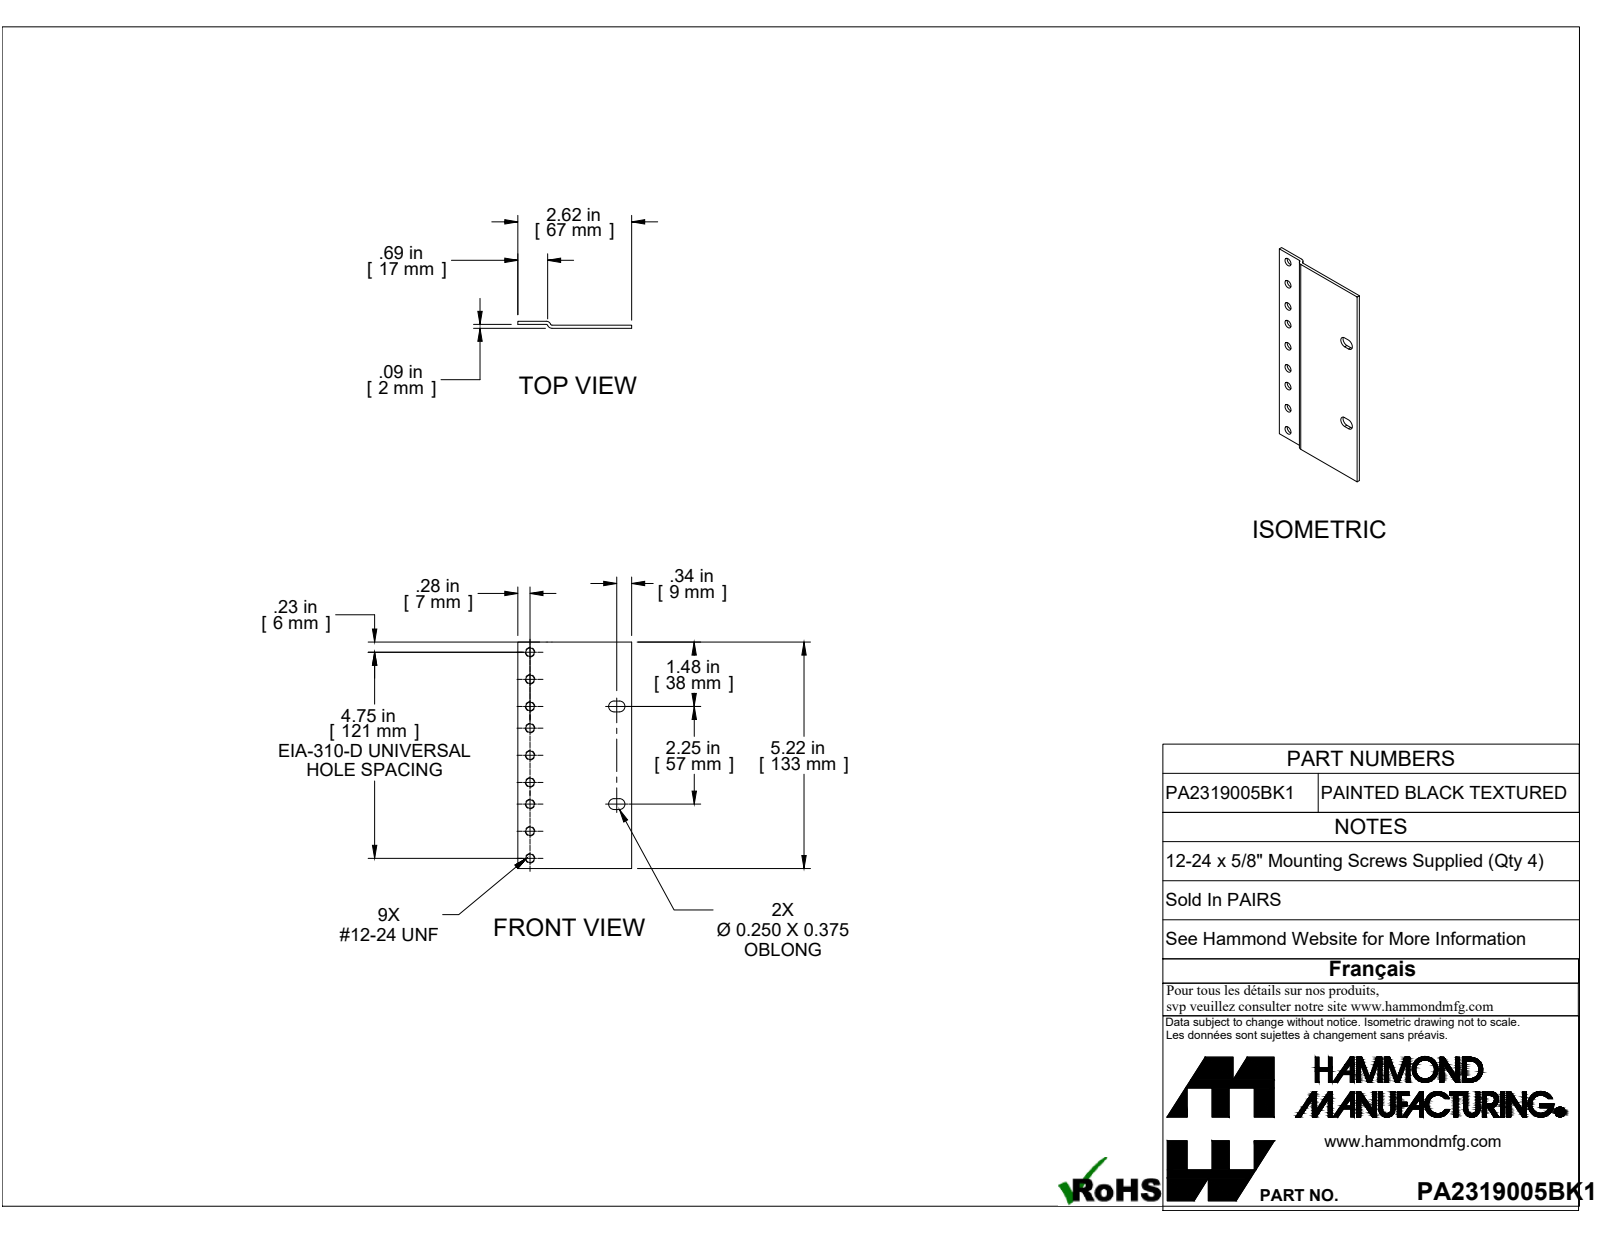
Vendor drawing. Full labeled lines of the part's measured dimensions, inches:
Part name (STEP PRODUCT): PA2319005BK1
STEP written by: SolidWorks 2019 (AUTOMOTIVE_DESIGN)
Units: inches
Bodies: 1 solid, 29 faces (12 planar, 17 cylindrical, 0 other)
Overall size (bounding box): 5.218 × 2.625 × 0.162
Volume: 0.976 in³ · Surface area: 28.71 in²
Round holes (diameter × count): ⌀0.159 ×9
Partial cylindrical surfaces — rounded edges, fillets, slot ends (radius × count): R0.125 ×4, R0.036 ×2, R0.108 ×2
Main face-to-face distances: 0.072, 0.09, 0.162, 0.018, 0.09, 0.072, 2.625, 5.218, 1.359, 1.609
Hole centre spacings: 0.625, 1.125, 1.75, 0.5, 0.625, 1.25, 1.75, 2.375
